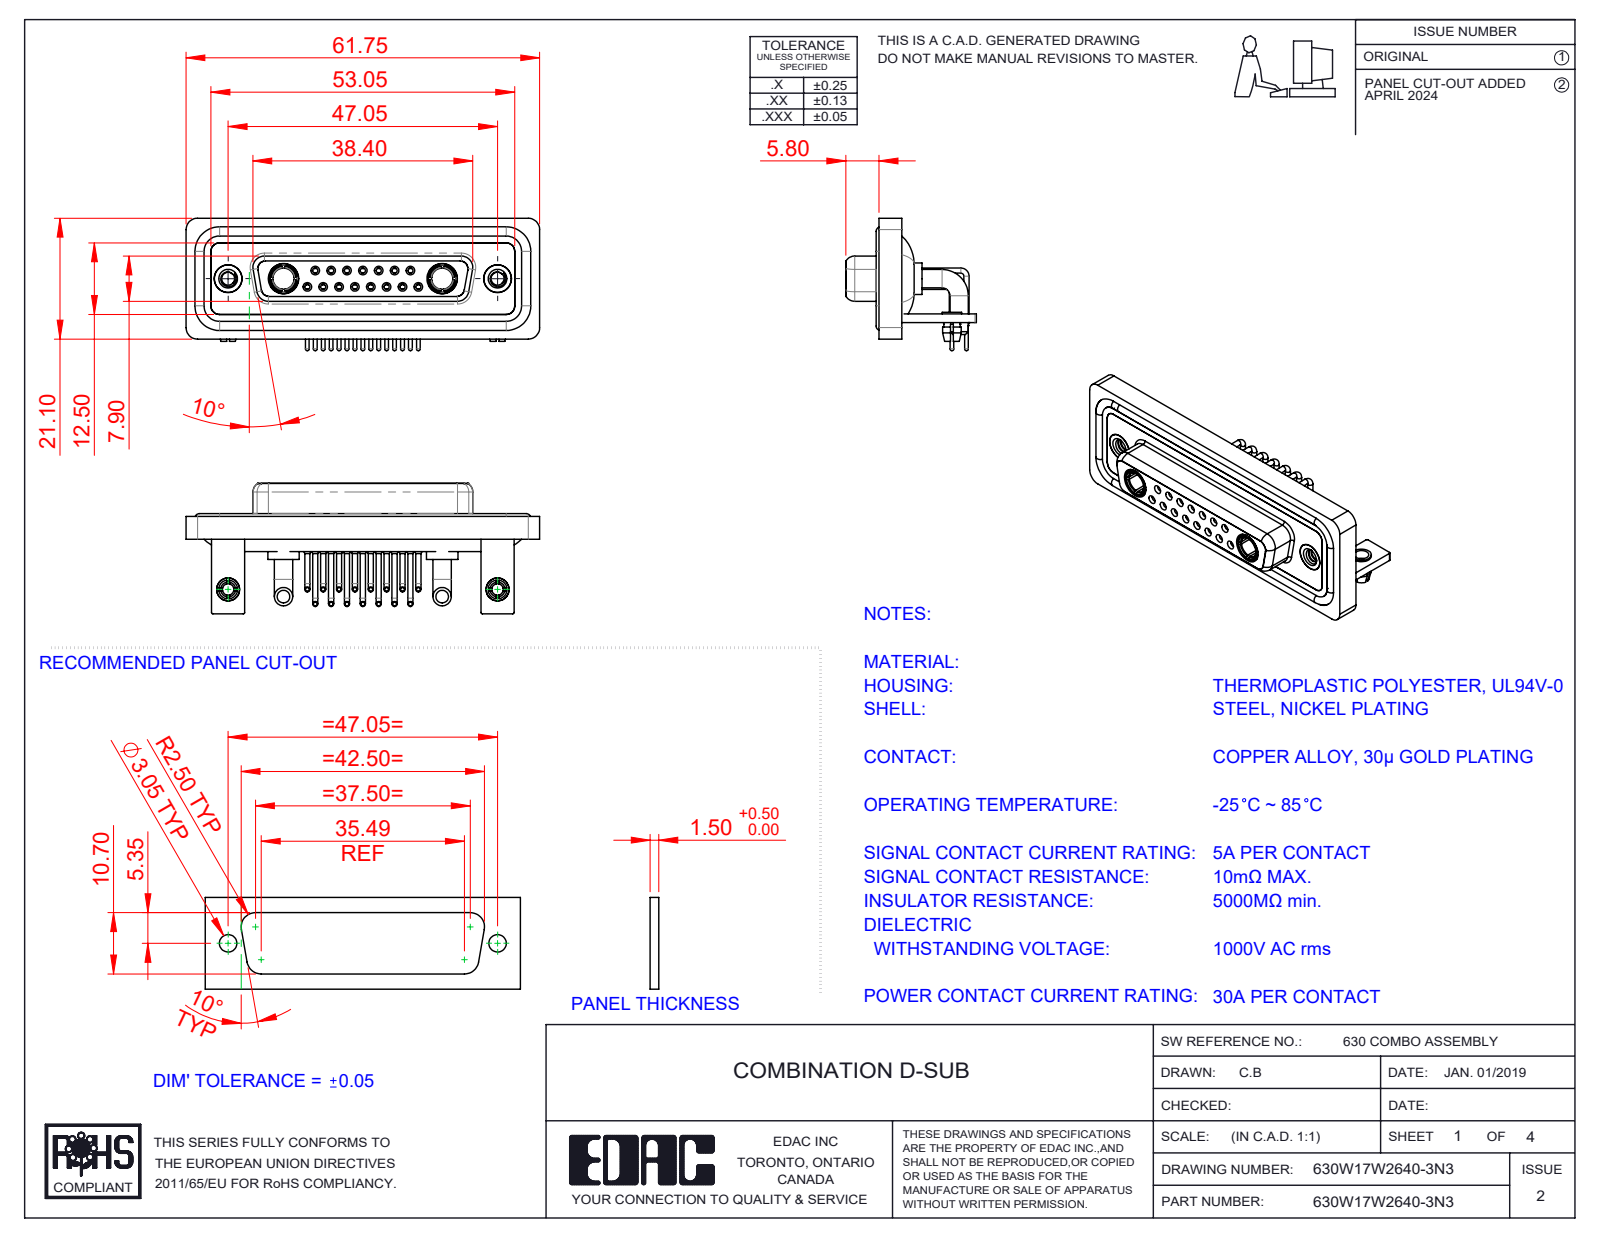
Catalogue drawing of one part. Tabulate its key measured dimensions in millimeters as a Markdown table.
| quantity | value |
| --- | --- |
| part name | 630Combo Contact Row 1_50 Contacts; 630Combo Shell Rear_25 Contacts; 630Combo Housing_17W2; 630Combo Waterproof Housing_25 Contacts (+7 more) |
| STEP written by | SolidWorks 2023 (CONFIG_CONTROL_DESIGN) |
| units | millimeters |
| bodies | 30 solids, 1477 faces (456 planar, 639 cylindrical, 382 other) |
| overall size | 61.75 × 23.12 × 22.8 |
| volume | 8 945 mm³ |
| surface area | 15 513 mm² |
| round holes (diameter × count) | 2 × 17, 0.9 × 15, 1.1 × 15, 1.5 × 15, 1.6 × 8, 1.7 × 7, 4.85 × 4, 2.26 × 2, 2.5 × 2, 3.2 × 2, 3.7 × 2, 4 × 2 |
| round bosses / shafts (diameter × count) | 0.9 × 15, 0.65 × 15, 1.6 × 11, 3.2 × 4, 5.5 × 2, 5.2 × 2, 4.96 × 2, 4.95 × 2 |
| partial cylindrical surfaces (radius × count) | 2 × 19, 1.5 × 18, 0.25 × 16, 1.35 × 8, 1.6 × 8, 0.5 × 5, 0.6 × 4, 0.65 × 4 |
| main face-to-face distances | 0.4, 1.8, 2.9, 3.7, 1.5, 4.1, 1.1, 1.4, 1.6, 3.1 |
| hole center spacings | 3.16, 2.77, 5.54, 8.31, 5.04, 7.49, 11.08, 5.03 |
